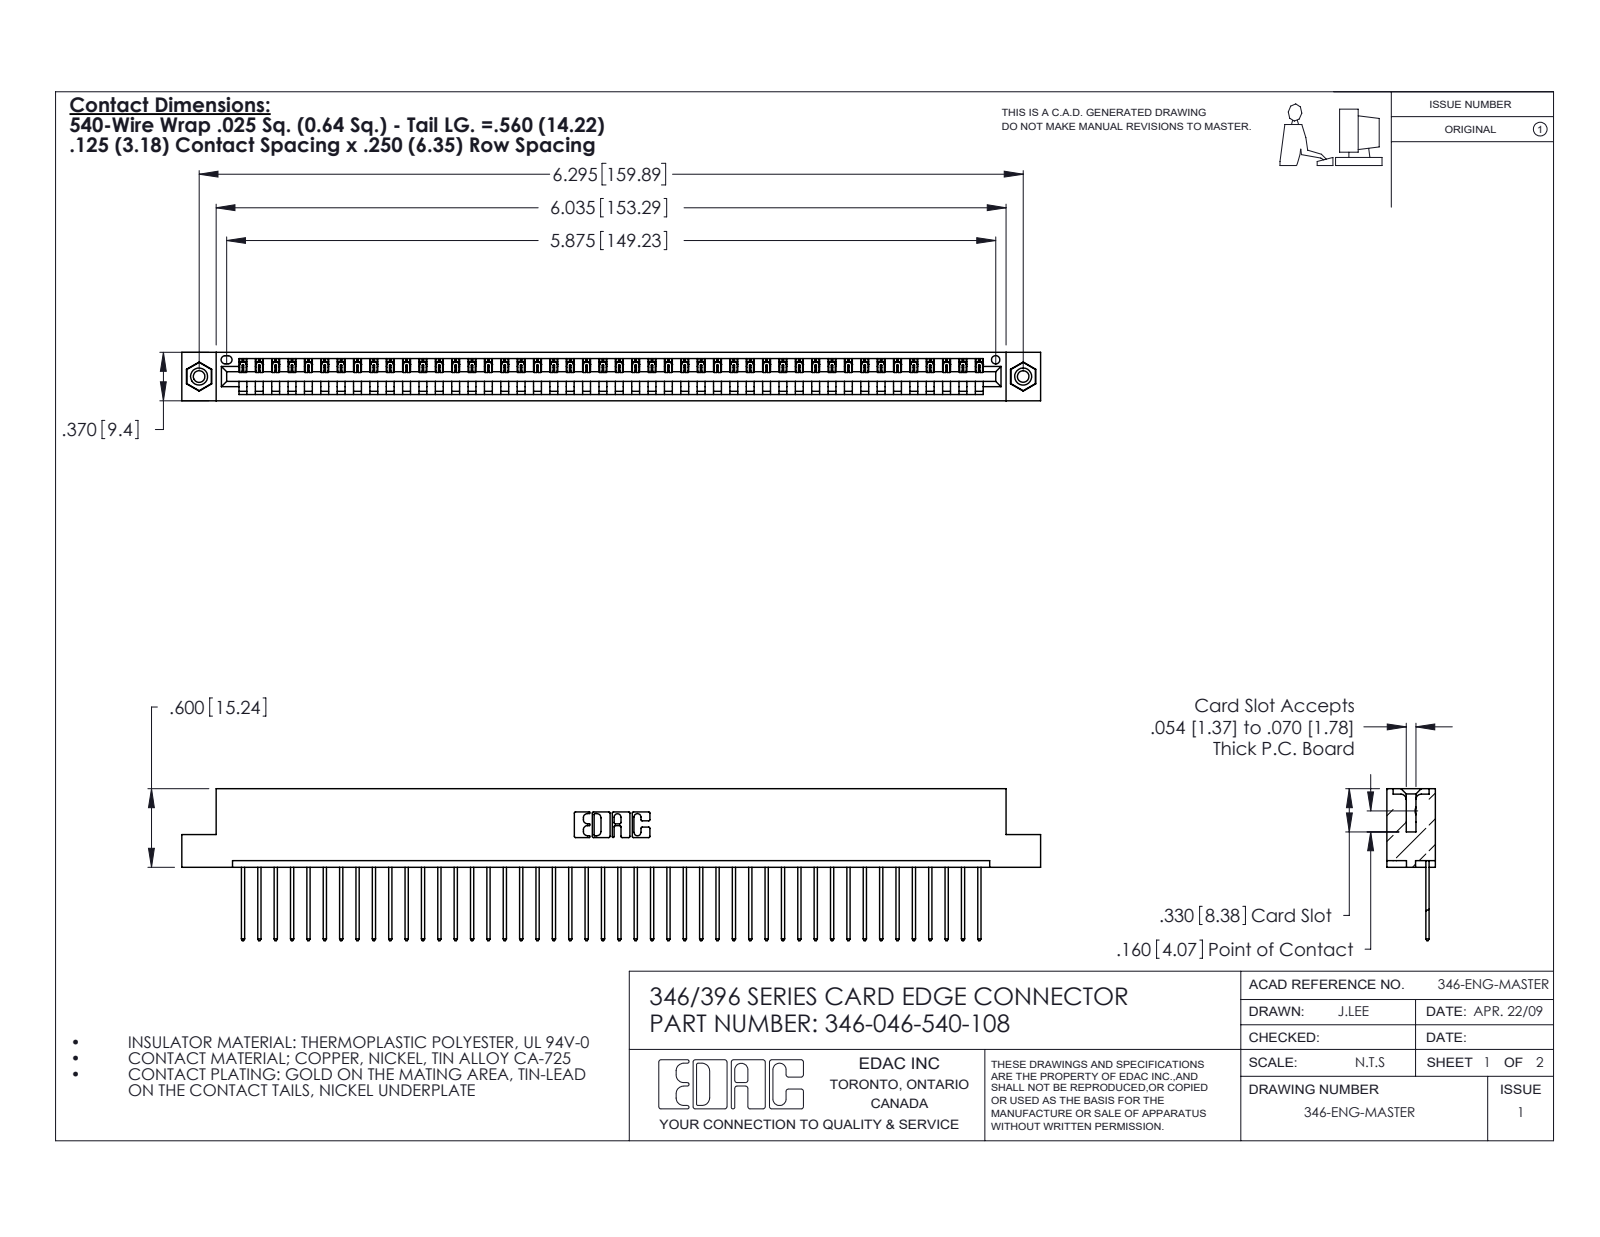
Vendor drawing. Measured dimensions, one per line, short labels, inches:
name: 346-046-540-108; 345-250-001_345-250-003-102; 345-292-001_345-293-140; 346 Part_Flush Mounting Lugs - 0.156 Dia-TI
written by: SolidWorks 2020 (CONFIG_CONTROL_DESIGN)
unit: in
bodies: 49 solids, 2850 faces (1948 planar, 886 cylindrical, 16 other)
size: 6.56 × 1.16 × 0.37
volume: 0.978 in³; area: 31.87 in²
holes: 2× ⌀0.089, 2× ⌀0.125, 2× ⌀0.156, 1× ⌀0.064
bosses: 2× ⌀0.155
rounds: 92× R0.006, 92× R0.01, 22× R0.01, 6× R0.007, 6× R0.031, 3× R0.026, 2× R0.031, 2× R0.04
face distances: 0.048, 0.322, 0.37, 0.25, 0.072, 0.298, 0.025, 0.148, 0.222, 0.1
hole spacings: 0.246, 6.086, 6.295
